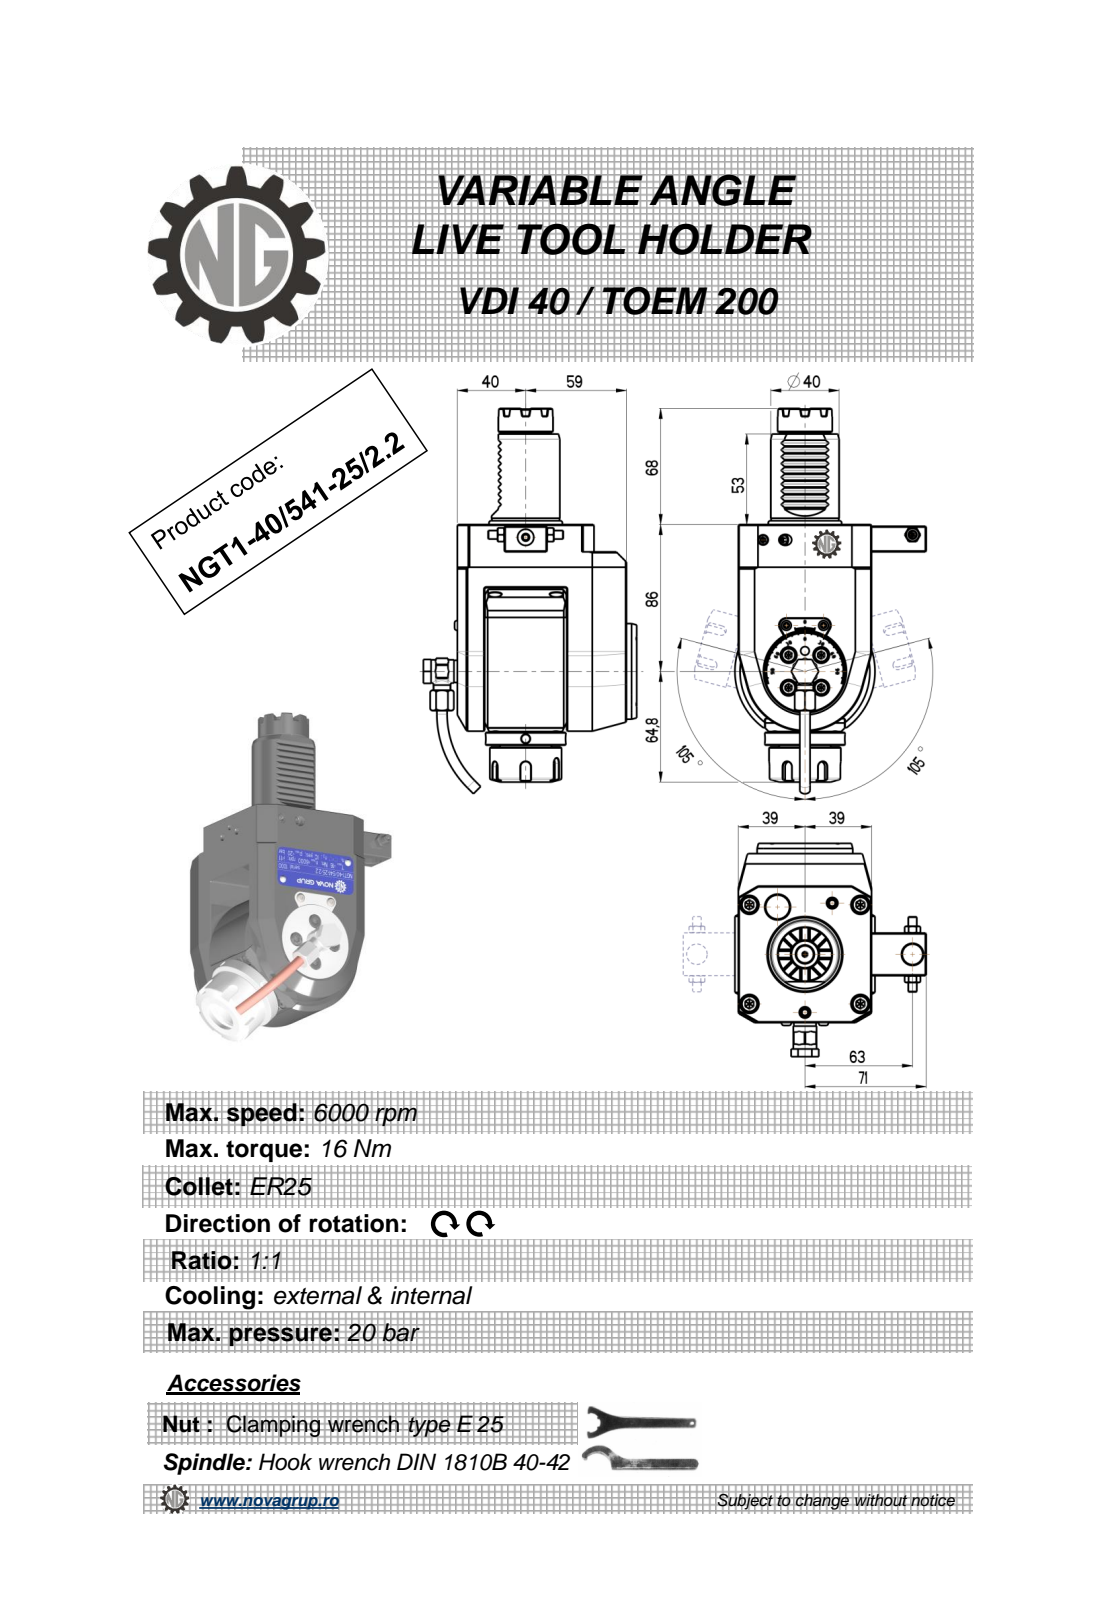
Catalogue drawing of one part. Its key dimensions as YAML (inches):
part_name: "NGT1_40_541_25_2_2"
step_written_by: "PRO/ENGINEER BY PARAMETRIC TECHNOLOGY CORPORATION, 2010280 (CONFIG_CONTROL_DESIGN)"
units: inches
bodies: {solids: 1, faces: 651, planar: 272, cylindrical: 144, other: 235}
overall_size: [8.885, 4.917, 4.409]
volume: 57.01
surface_area: 132.2
round_holes:
  - {diameter: 0.157, count: 3}
  - {diameter: 0.197, count: 2}
  - {diameter: 0.118, count: 1}
  - {diameter: 0.165, count: 1}
  - {diameter: 0.177, count: 1}
  - {diameter: 0.244, count: 1}
  - {diameter: 0.354, count: 1}
  - {diameter: 0.374, count: 1}
  - {diameter: 0.433, count: 1}
  - {diameter: 0.472, count: 1}
  - {diameter: 0.799, count: 1}
round_bosses_or_shafts:
  - {diameter: 0.394, count: 2}
  - {diameter: 0.236, count: 2}
  - {diameter: 0.224, count: 2}
  - {diameter: 2.205, count: 1}
  - {diameter: 1.85, count: 1}
  - {diameter: 1.654, count: 1}
  - {diameter: 1.575, count: 1}
  - {diameter: 1.378, count: 1}
partial_cylinders:
  - {radius: 0.01, count: 12}
  - {radius: 0.012, count: 10}
  - {radius: 0.118, count: 5}
  - {radius: 0.02, count: 4}
  - {radius: 0.039, count: 2}
  - {radius: 0.394, count: 2}
  - {radius: 0.303, count: 1}
  - {radius: 0.339, count: 1}
face_to_face_distances: [0.63, 1.457, 3.071, 3.898, 2.52, 4.134, 0.236, 0.827, 0.039, 3.504]
hole_center_spacings: [0.016, 1.553, 1.929, 1.945, 2.48, 3.142, 3.152, 4.009]
